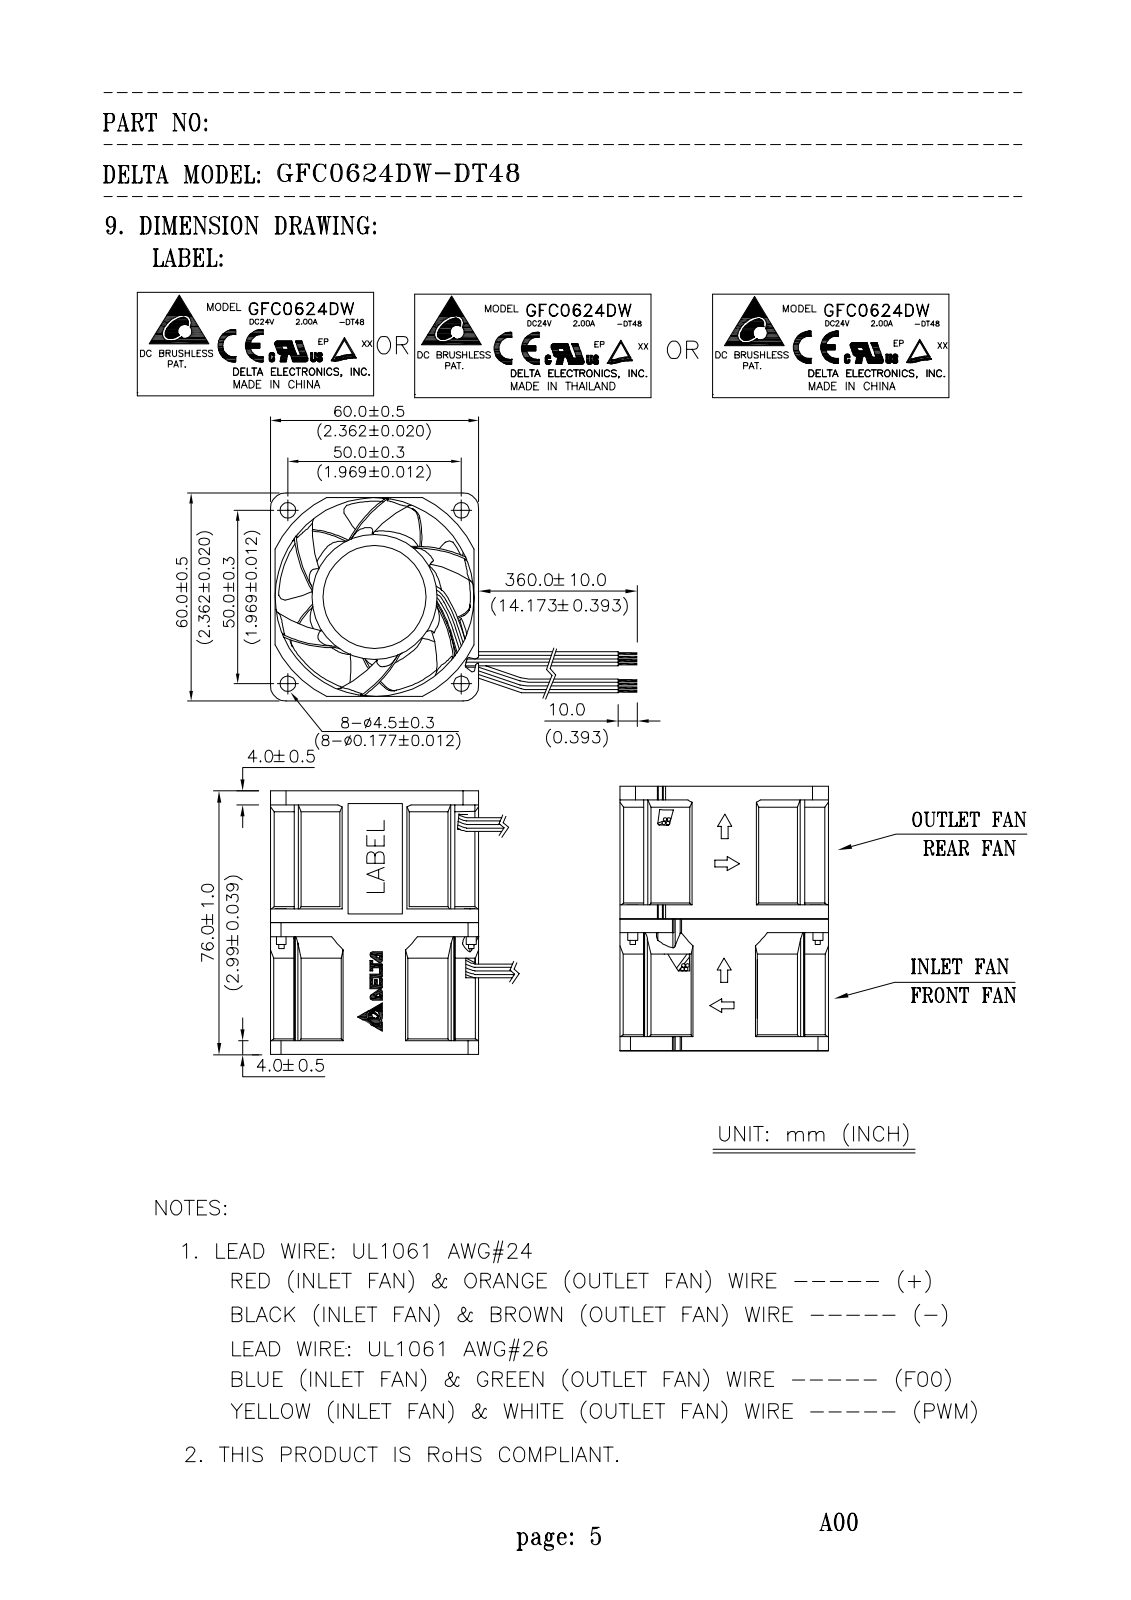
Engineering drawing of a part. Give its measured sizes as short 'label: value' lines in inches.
name: PRT0001_AF0; PRT0002_AF0; ASM0001_ASM
written by: CREO PARAMETRIC BY PTC INC, 2015080 (CONFIG_CONTROL_DESIGN)
unit: in
bodies: 2 solids, 411 faces (270 planar, 108 cylindrical, 33 other)
size: 76 × 60.5 × 60
volume: 233 563 in³; area: 33 478 in²
holes: 4× ⌀4.5
rounds: 8× R0.6, 7× R0.5, 4× R0.7, 4× R3, 4× R4.5, 2× R1.702, 1× R0.2, 1× R0.254
face distances: 38, 60, 76, 4, 34, 42, 72, 30, 8, 68
hole spacings: 50, 70.711
